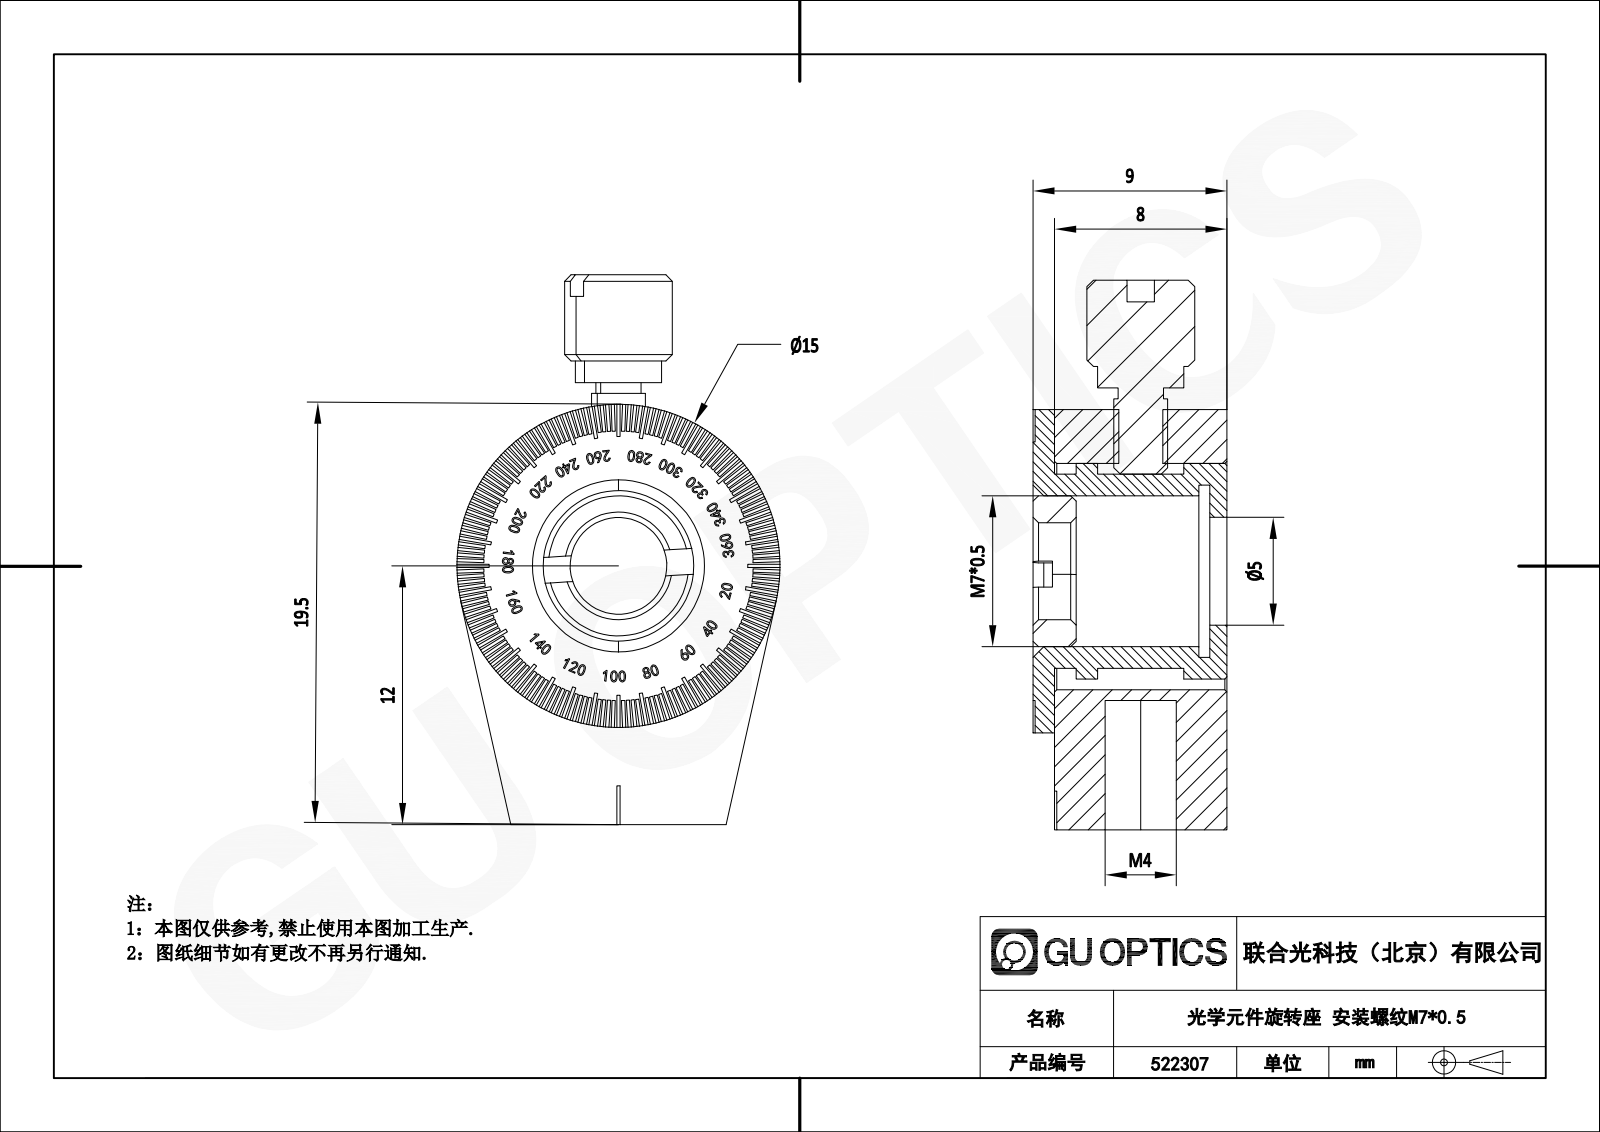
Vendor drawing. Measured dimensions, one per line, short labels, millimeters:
name: 一体式手拧螺丝_M2.5X4; ZFK透镜卡环压圈_1.8.5.7-ZFK-K6
written by: SolidWorks 2021 (CONFIG_CONTROL_DESIGN)
unit: mm
bodies: 4 solids, 1226 faces (991 planar, 37 cylindrical, 198 other)
size: 25.5 × 15 × 9
volume: 1 745 mm³; area: 2 289 mm²
holes: 1× ⌀2.05, 1× ⌀3.3, 1× ⌀4.5, 1× ⌀5, 1× ⌀7, 1× ⌀8
bosses: 1× ⌀15, 1× ⌀10, 1× ⌀9, 1× ⌀5, 1× ⌀4, 1× ⌀2.5, 1× ⌀2.1
rounds: 1× R4
face distances: 8, 1, 9, 2, 7, 0.9, 6, 8.9, 0.8, 8.1
